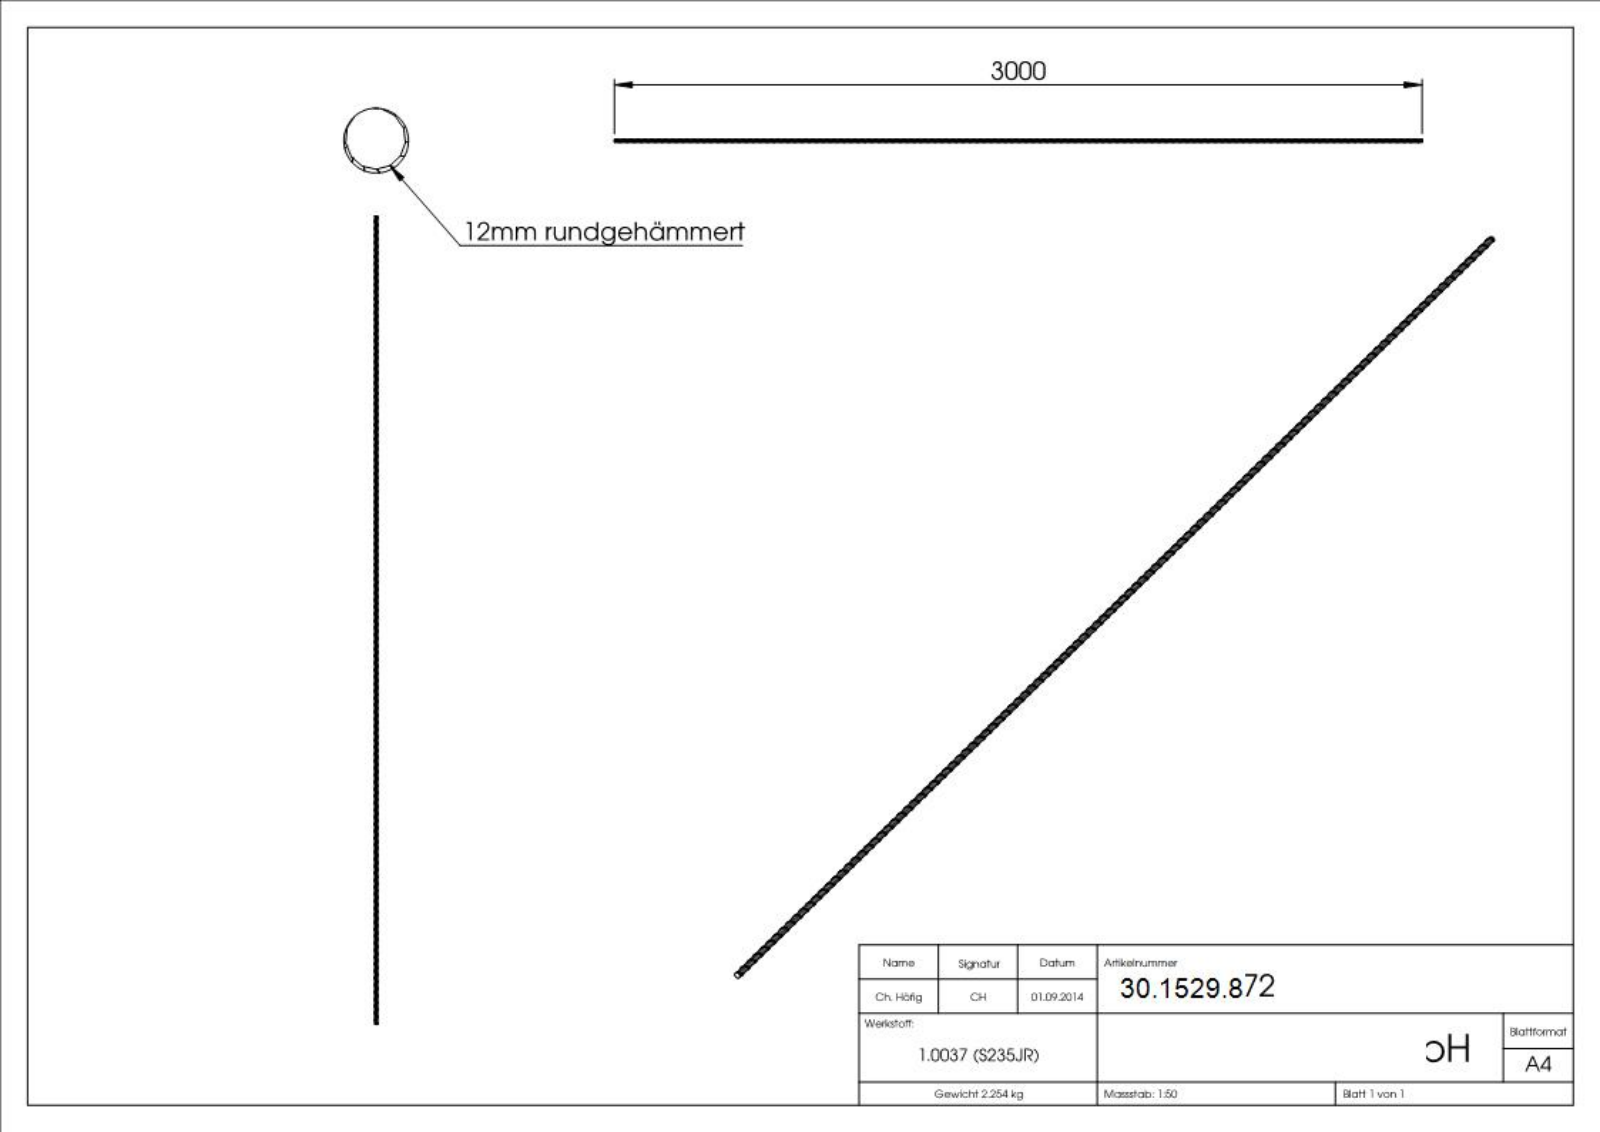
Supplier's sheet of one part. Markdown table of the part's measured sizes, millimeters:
| quantity | value |
| --- | --- |
| part name | 6972 |
| STEP written by | SolidWorks 2015 (CONFIG_CONTROL_DESIGN) |
| units | millimeters |
| bodies | 1 solid, 3476 faces (298 planar, 3130 cylindrical, 48 other) |
| overall size | 3000 × 12 × 12 |
| volume | 288 999 mm³ |
| surface area | 105 793 mm² |
| round bosses / shafts (diameter × count) | 12 × 1 |
| partial cylindrical surfaces (radius × count) | 78.62 × 1512 |
| main face-to-face distances | 3000, 0.5, 2999.5, 0.75, 1.78, 2.69, 0.44, 0.98, 0.91, 0.82 |
